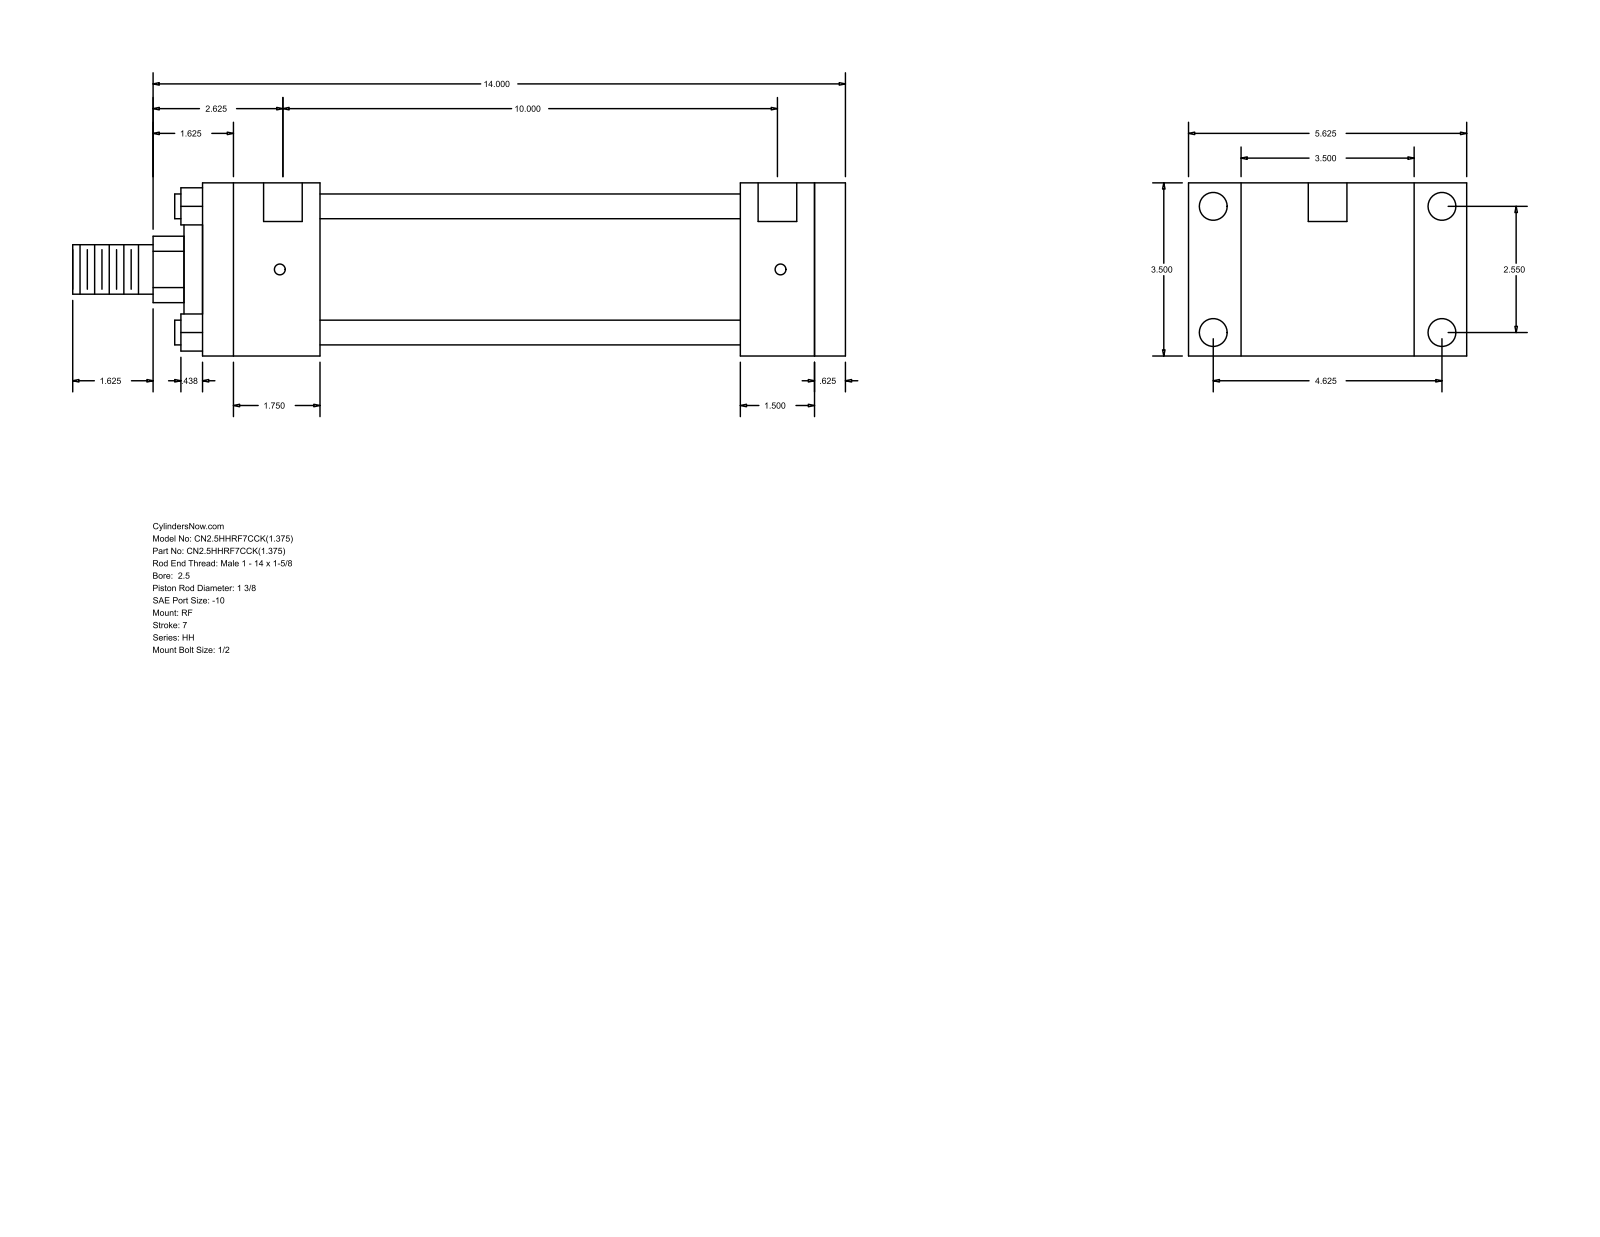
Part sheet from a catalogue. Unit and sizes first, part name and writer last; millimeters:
Units: millimetres
Overall size (bounding box): 396.88 × 142.88 × 88.9
Round holes (diameter × count): ⌀5.56 ×4, ⌀14.3 ×4, ⌀19.84 ×2
Round bosses / shafts (diameter × count): ⌀12.7 ×4, ⌀73.03 ×1, ⌀50.8 ×1, ⌀34.92 ×1, ⌀25.4 ×1
Partial cylindrical surfaces — rounded edges, fillets, slot ends (radius × count): R17.06 ×1
Main face-to-face distances: 88.9, 330.2, 314.33, 15.87, 60.32, 254.01, 269.88, 276.22, 215.9, 38.11
Hole centre spacings: 1.58, 64.76, 117.48, 134.15, 255.59, 257.17, 254.01
Bodies: 0 solids, 92 faces (64 planar, 28 cylindrical, 0 other)
Part name (STEP PRODUCT): HH_RF__0250_1.375
STEP written by: GSSL Pune (CONFIG_CONTROL_DESIGN)
